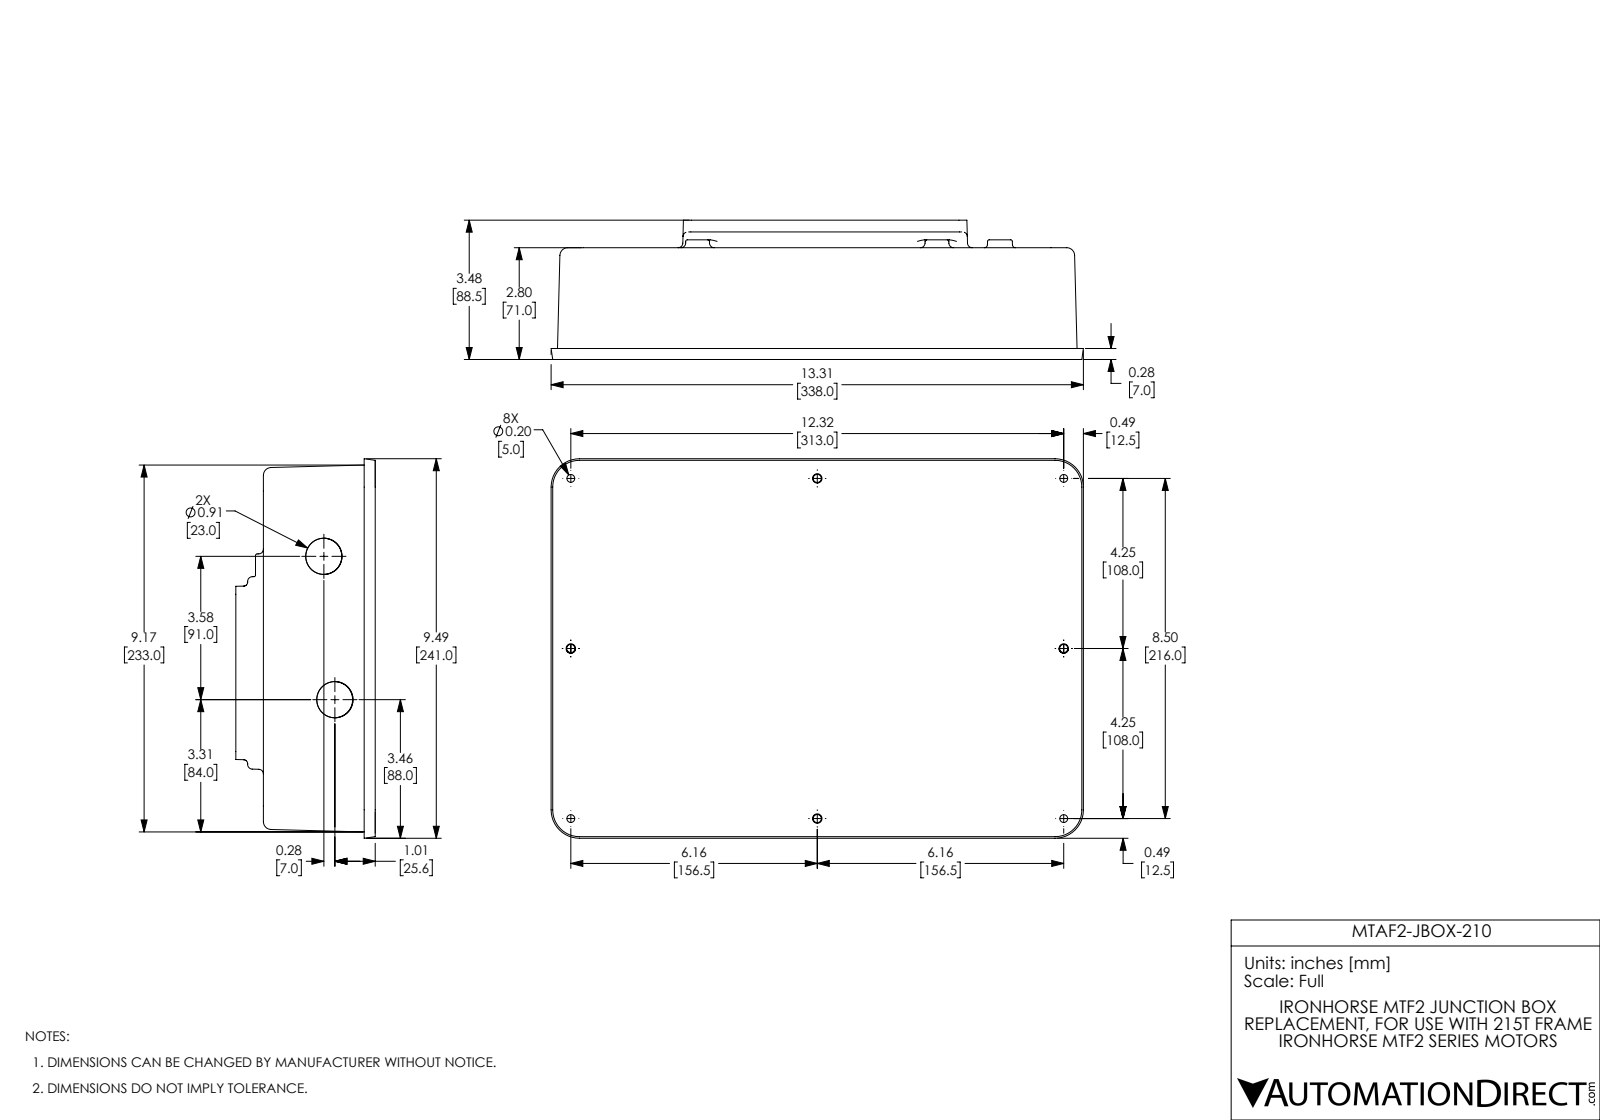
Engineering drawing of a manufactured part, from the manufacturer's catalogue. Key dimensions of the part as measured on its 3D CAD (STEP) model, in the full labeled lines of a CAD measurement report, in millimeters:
Part name (STEP PRODUCT): MTAF2-JBOX-210 coord
STEP written by: SolidWorks 2017 (AUTOMOTIVE_DESIGN)
Units: millimetres
Bodies: 2 solids, 577 faces (82 planar, 159 cylindrical, 336 other)
Overall size (bounding box): 338 × 241 × 88.5
Volume: 954 400 mm³ · Surface area: 477 400 mm²
Round holes (diameter × count): ⌀5.2 ×9, ⌀5 ×7, ⌀6 ×4, ⌀23 ×2
Partial cylindrical surfaces — rounded edges, fillets, slot ends (radius × count): R1 ×22, R5 ×20, R3 ×19, R0.5 ×16, R1.5 ×8, R15 ×8, R2 ×4, R2.5 ×2
Main face-to-face distances: 1, 5, 70, 71, 4.1, 65, 66, 17.5, 22.5, 87.5
Hole centre spacings: 108, 156.5, 190.1, 266.8, 331.1, 216, 313, 65.2
